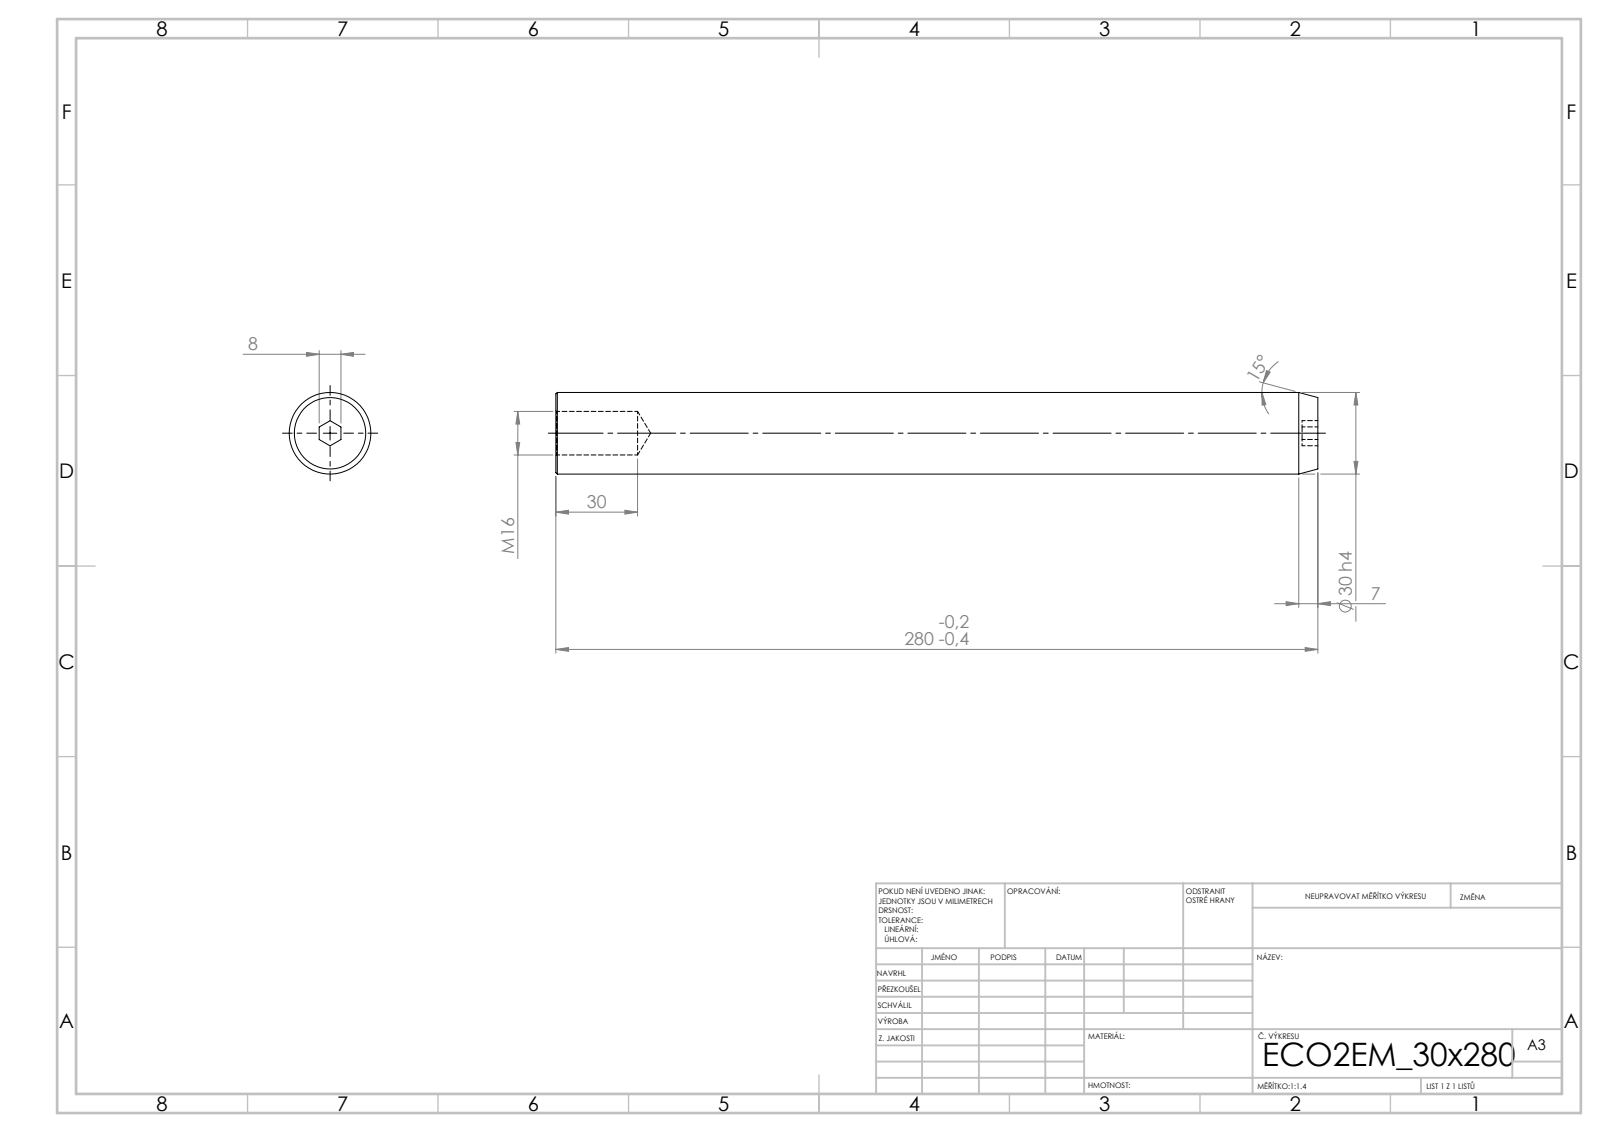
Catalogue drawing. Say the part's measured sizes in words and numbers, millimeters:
Its 3-D file was written by "SolidWorks 2019 (CONFIG_CONTROL_DESIGN)". It is 1 solid with 21 faces: 9 planar, 4 cylindrical and 8 other. Overall it measures 280 by 30 by 30 millimeters. Its volume is 190 639 cubic millimeters and its surface area 29 286 square millimeters. Round holes: 1 of diameter 16. Round bosses or shafts: 1 of diameter 30. The main face-to-face distances are 280, 8, 5.8, 274.2.
